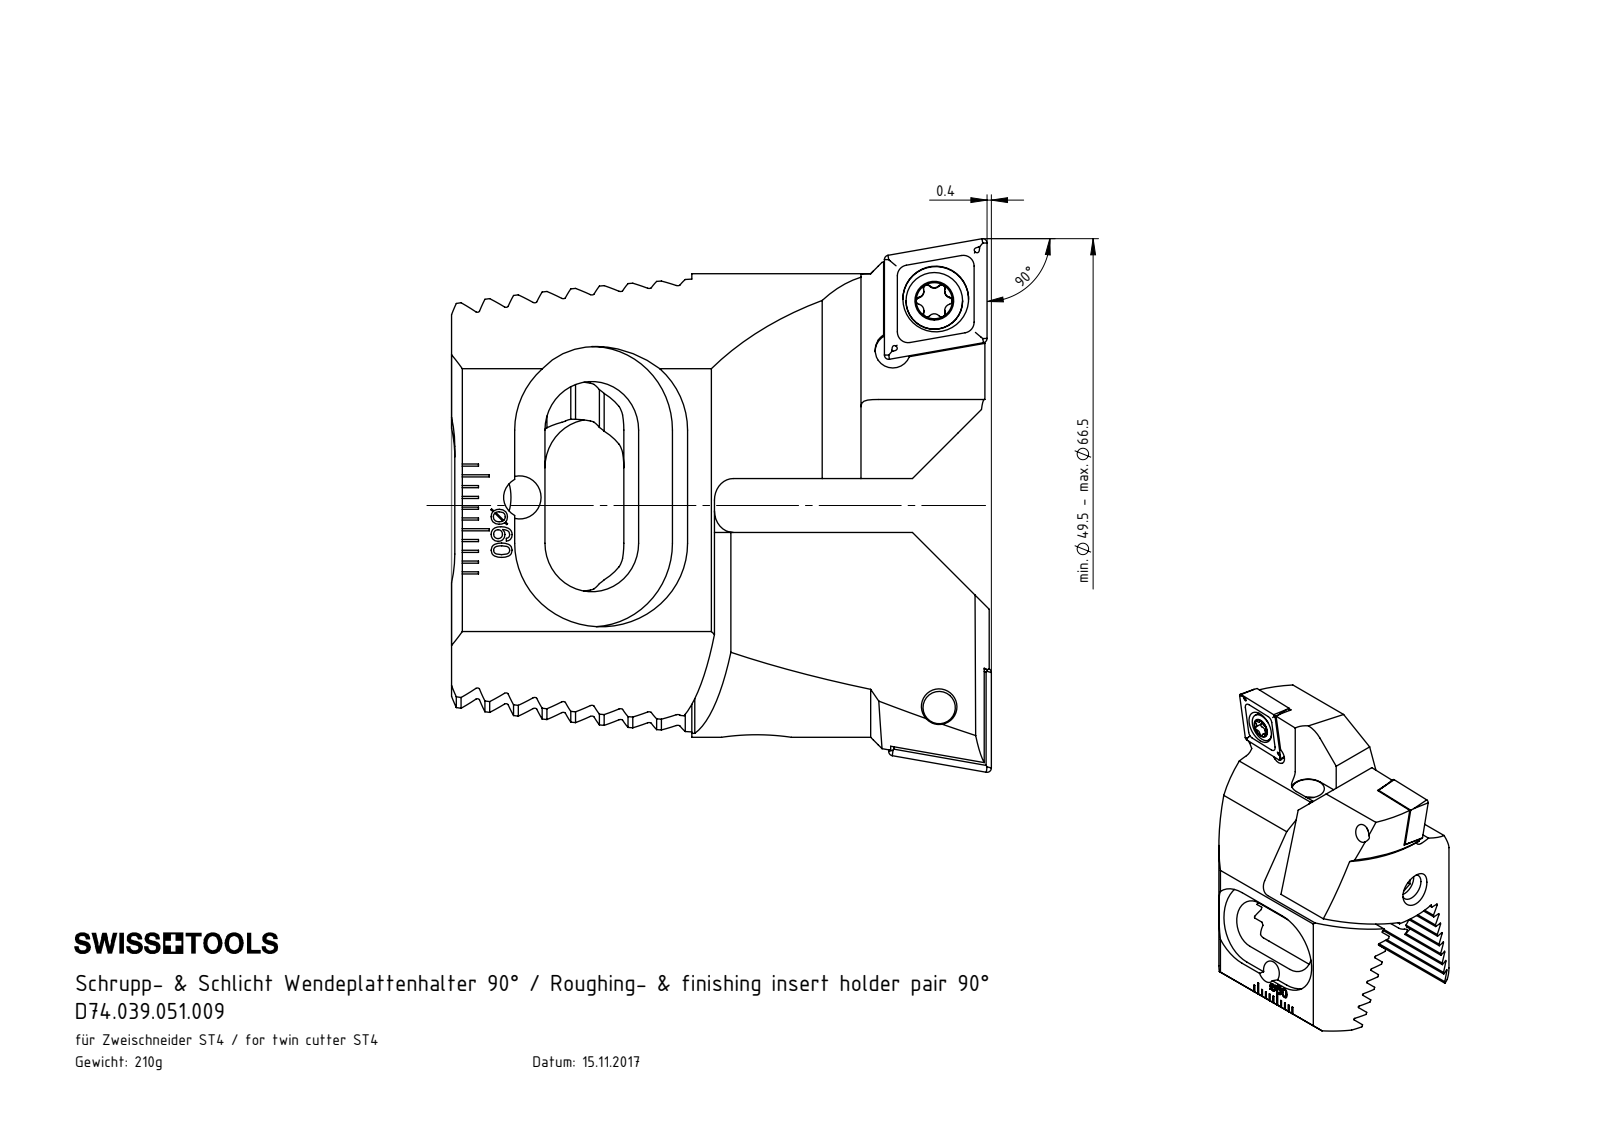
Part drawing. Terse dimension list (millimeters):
name: ZC4-xxx.001.028_A_versetzt mit FV; WCB-ER2.001.009_A; CCMT09T304; ZC4-xxx.001.028_A (+3 more)
written by: SolidWorks 2017 (CONFIG_CONTROL_DESIGN)
unit: mm
bodies: 8 solids, 657 faces (343 planar, 132 cylindrical, 182 other)
size: 50.1 × 49.5 × 34.2
volume: 26 842 mm³; area: 13 156 mm²
holes: 4× ⌀3.3, 2× ⌀4.4, 2× ⌀6.1, 1× ⌀1.6, 1× ⌀2.5, 1× ⌀4, 1× ⌀5, 1× ⌀6
bosses: 3× ⌀4, 2× ⌀5.25, 1× ⌀6, 1× ⌀3, 1× ⌀2
rounds: 16× R0.2, 12× R0.34, 12× R0.59, 4× R2, 4× R4.5, 4× R7.75, 4× R12, 4× R21
face distances: 2.38, 4.76, 11.91, 9.53, 14.29, 7.15, 5.5, 4.77, 7.14, 0.5
hole spacings: 6.19, 33.71, 5.99, 6.07, 12, 28.78, 33.55, 33.81
